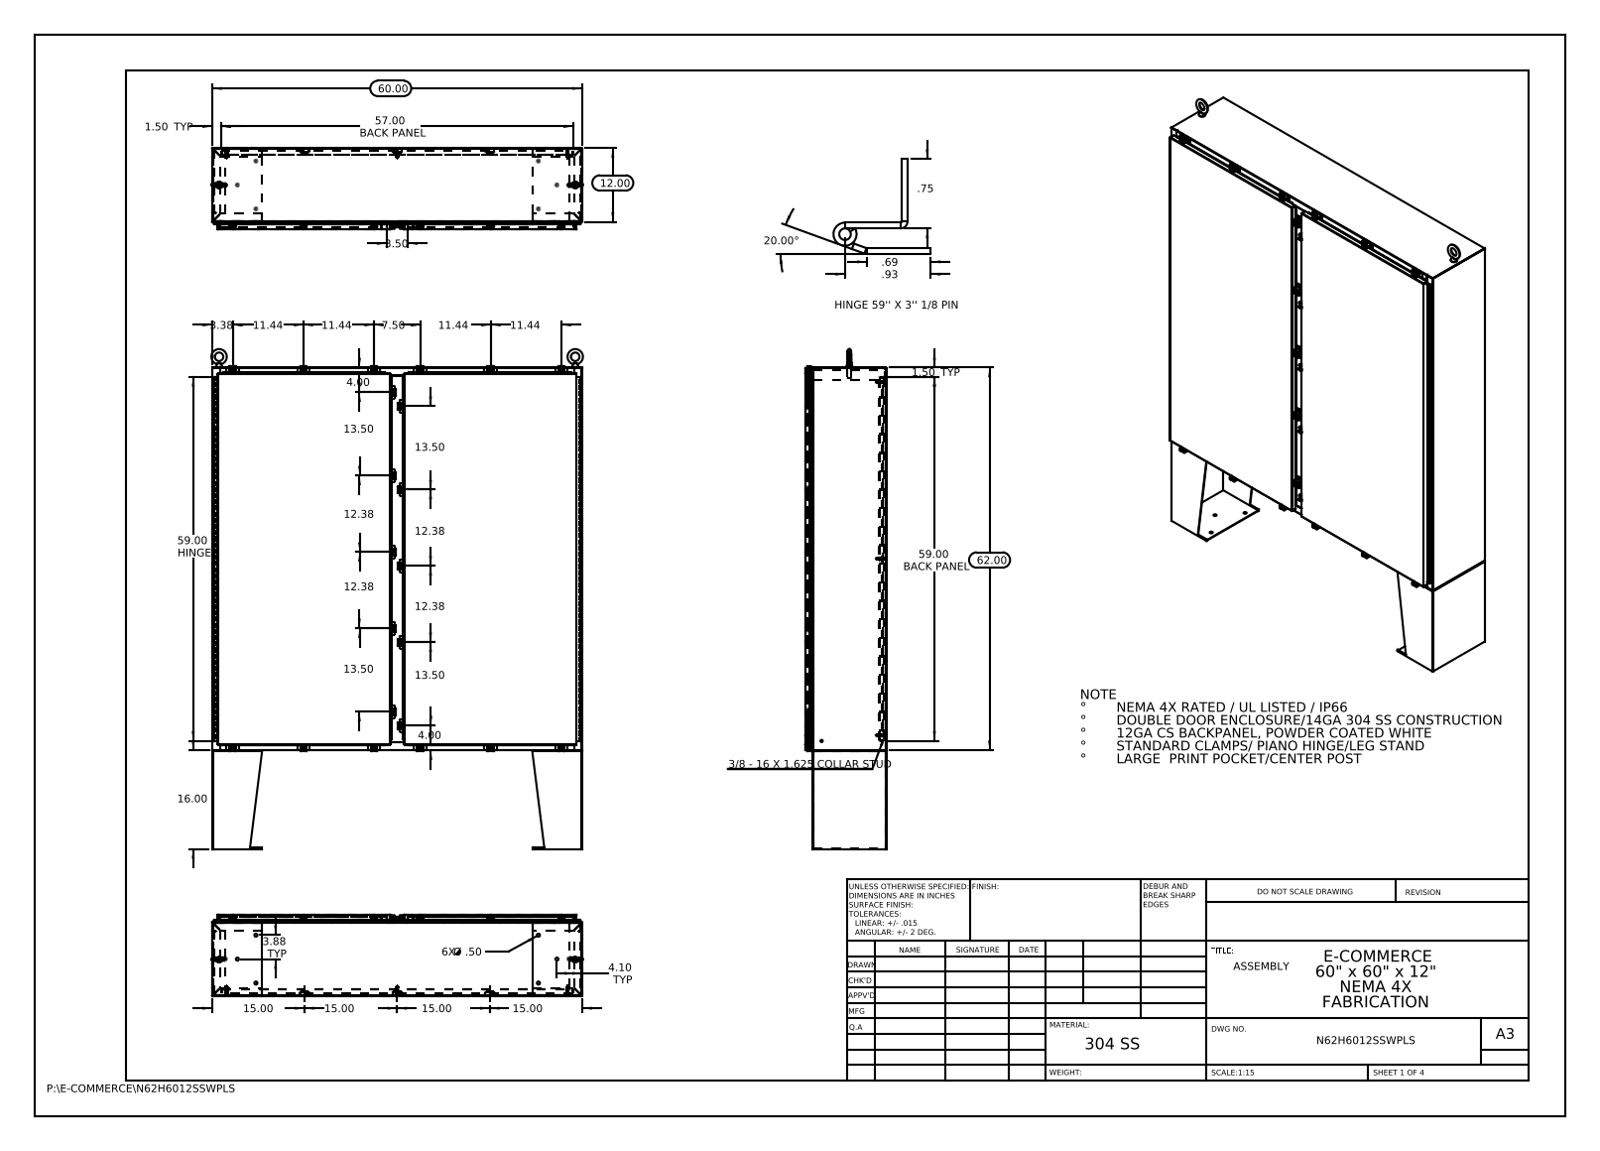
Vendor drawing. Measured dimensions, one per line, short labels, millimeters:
name: Quarter-20 CD Stud; N62H6012SSWPLS FSD_DD - LSK - Stand; Standard Clamps; N62H6012SSWPLS Eye-Bolt_Stiffener (+8 more)
written by: SolidWorks 2013 (CONFIG_CONTROL_DESIGN)
unit: mm
bodies: 144 solids, 6444 faces (3354 planar, 2762 cylindrical, 328 other)
size: 2057.4 × 1529.7 × 335.3
volume: 23 010 000 mm³; area: 21 970 000 mm²
holes: 22× ⌀5.4, 22× ⌀6.6, 14× ⌀12.7, 4× ⌀19.1, 2× ⌀3.2, 2× ⌀3.2
bosses: 24× ⌀6.4, 22× ⌀12.7, 22× ⌀10.1, 10× ⌀15.9, 8× ⌀9.5, 8× ⌀8.4, 3× ⌀8, 3× ⌀6
rounds: 96× R1.5, 48× R0.3, 44× R3, 44× R3.6, 40× R2.2, 32× R1.3, 32× R2, 32× R2.3
face distances: 1.9, 333.4, 2.6, 27.3, 331.5, 25.4, 308, 335.3, 306.1, 29.9
hole spacings: 1560.3, 1740.7, 66.2, 109, 180.8, 181.3, 290.5, 290.5
